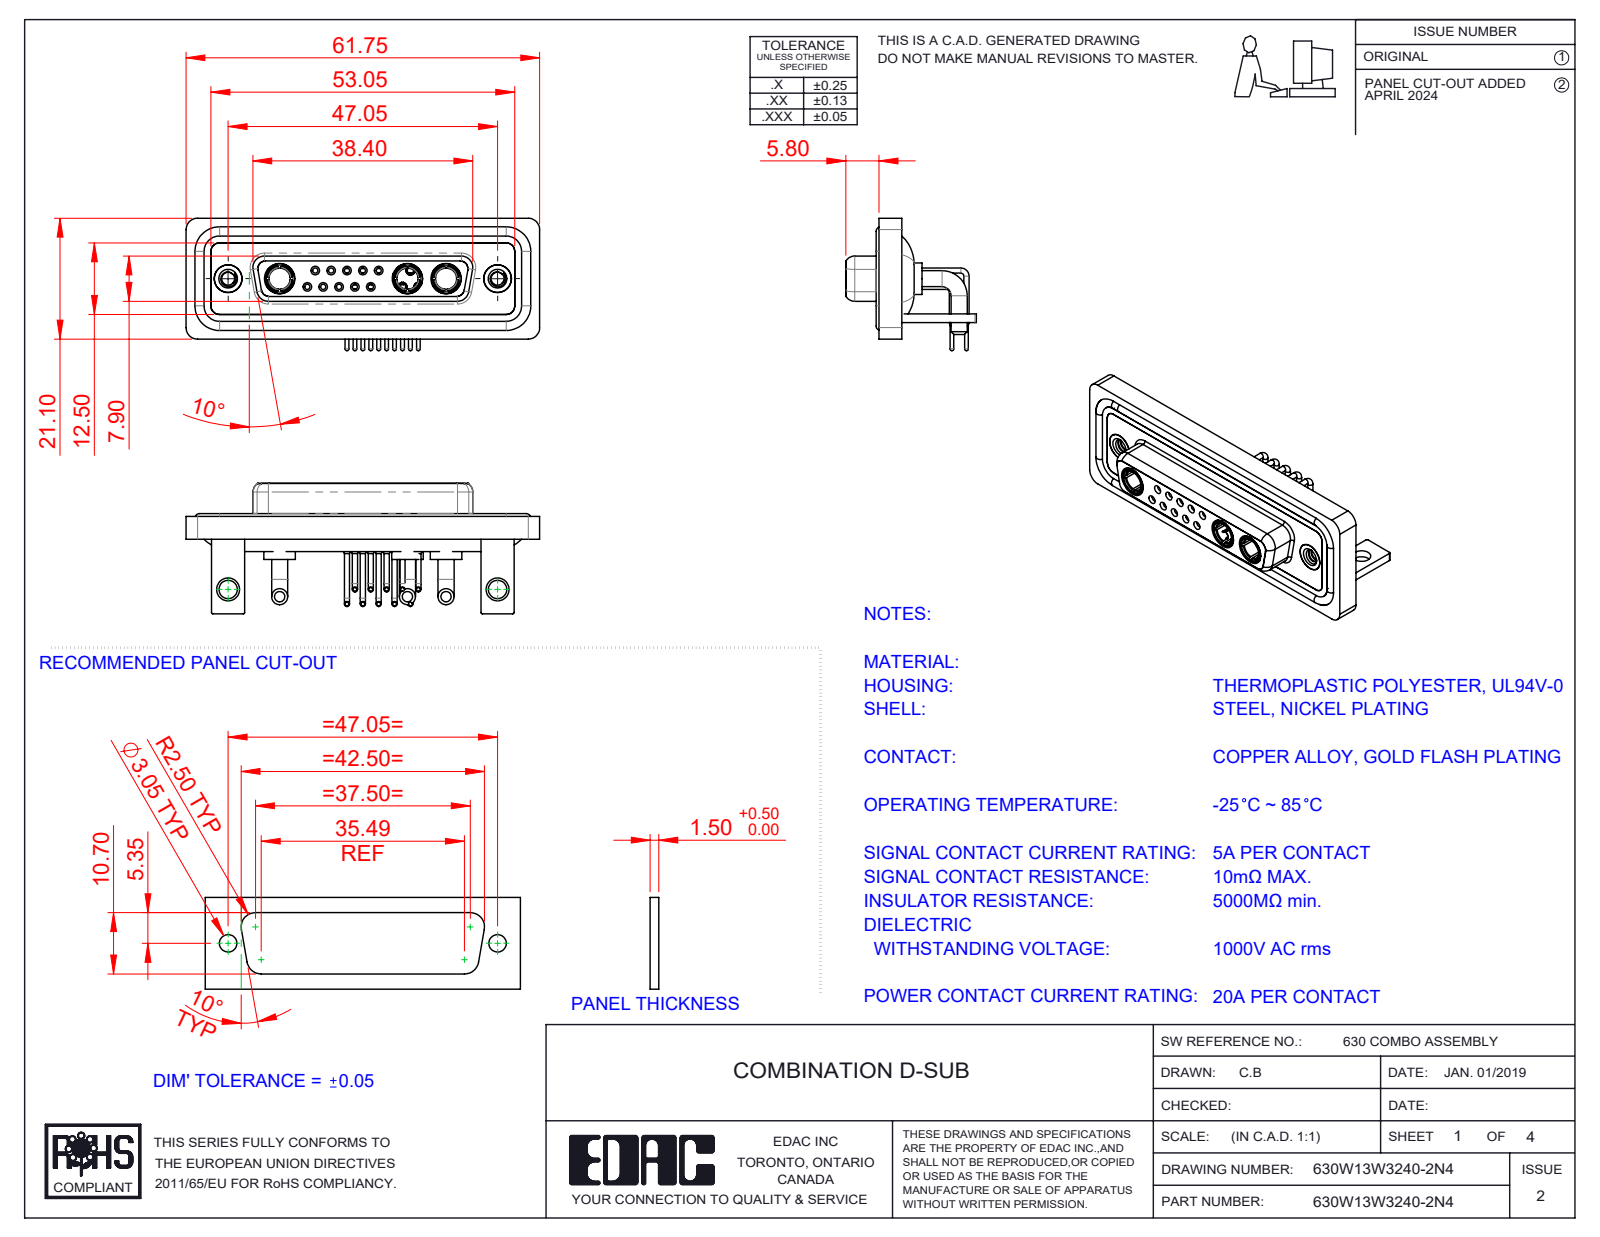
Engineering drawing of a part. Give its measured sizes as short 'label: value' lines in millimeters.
name: 630Combo Shell Rear_25 Contacts; Power Socket_20A RA; 630Combo Waterproof Housing_25 Contacts; 630Combo Shell Front_25 Contacts (+6 more)
written by: SolidWorks 2023 (CONFIG_CONTROL_DESIGN)
unit: mm
bodies: 25 solids, 1198 faces (362 planar, 517 cylindrical, 319 other)
size: 61.75 × 23.12 × 22.8
volume: 8 837 mm³; area: 15 032 mm²
holes: 10× ⌀0.9, 10× ⌀1.1, 10× ⌀1.5, 10× ⌀2, 5× ⌀1.6, 5× ⌀1.7, 5× ⌀4.85, 3× ⌀3.7, 3× ⌀5.3, 2× ⌀2.26, 2× ⌀3.2, 2× ⌀4
bosses: 15× ⌀0.9, 12× ⌀1.6, 10× ⌀0.65, 6× ⌀2.8, 5× ⌀2, 5× ⌀1.5, 3× ⌀5.5, 3× ⌀5.2
rounds: 19× R2, 18× R1.5, 16× R0.25, 8× R1.35, 8× R1.6, 5× R0.5, 4× R0.6, 4× R0.65
face distances: 0.4, 1.8, 2.9, 3.7, 1.5, 4.1, 1.1, 1.4, 1.6, 3.1
hole spacings: 3.16, 2.77, 5.54, 5.04, 8.31, 5.03, 7.49, 11.08
